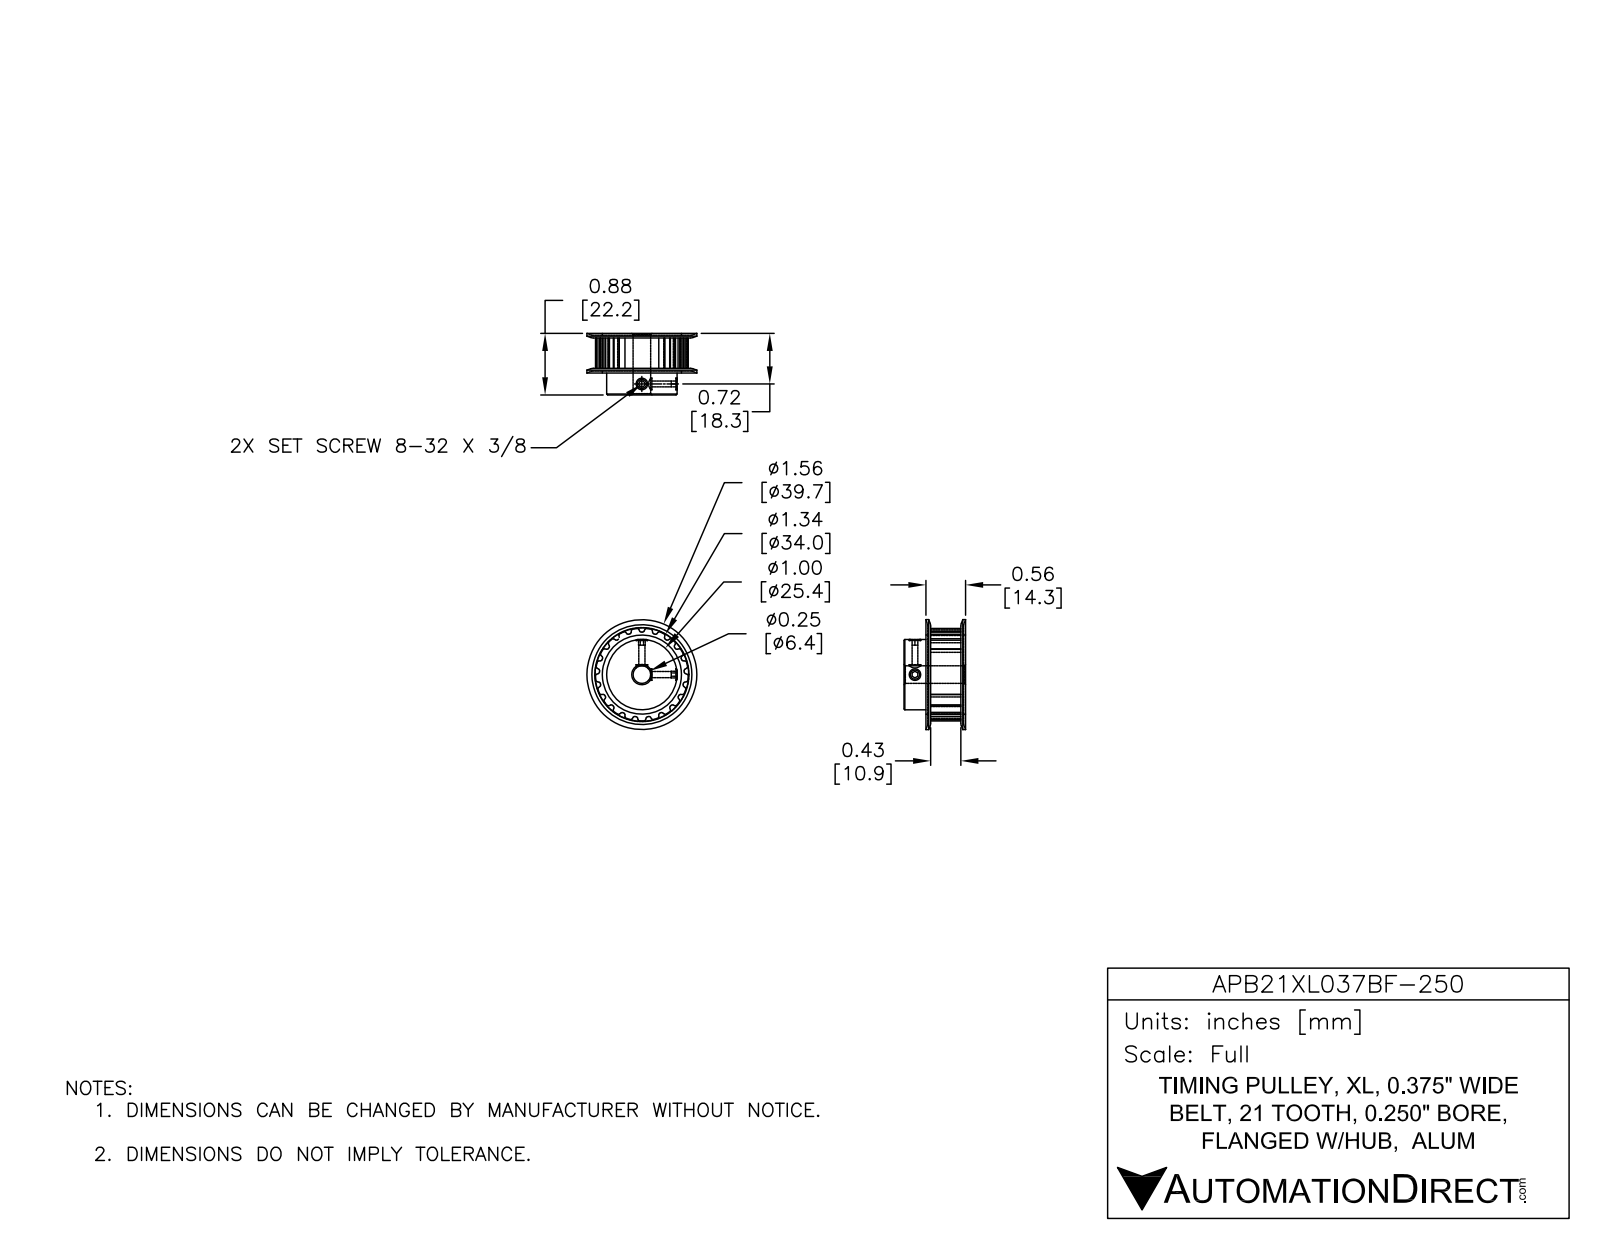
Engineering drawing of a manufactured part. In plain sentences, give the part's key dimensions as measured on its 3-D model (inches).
The part is named "APB21XL037BF-250". Its 3-D file was written by "SolidWorks 2014 (AUTOMOTIVE_DESIGN)". It is 1 solid with 223 faces: 69 planar, 132 cylindrical and 22 other. Overall it measures 1.563 by 1.563 by 0.875 inches. Its volume is 0.924 cubic inches and its surface area 9.666 square inches. Round holes: 2 of diameter 0.088, 1 of diameter 0.25. Round bosses or shafts: 1 of diameter 1. Partial cylindrical surfaces (rounded edges, fillets, slot ends): 84 of radius 0.015, 1 of radius 0.604. The main face-to-face distances are 0.033, 0.495, 0.875, 0.528, 0.348, 0.843, 0.462, 0.38, 0.065, 0.032.
